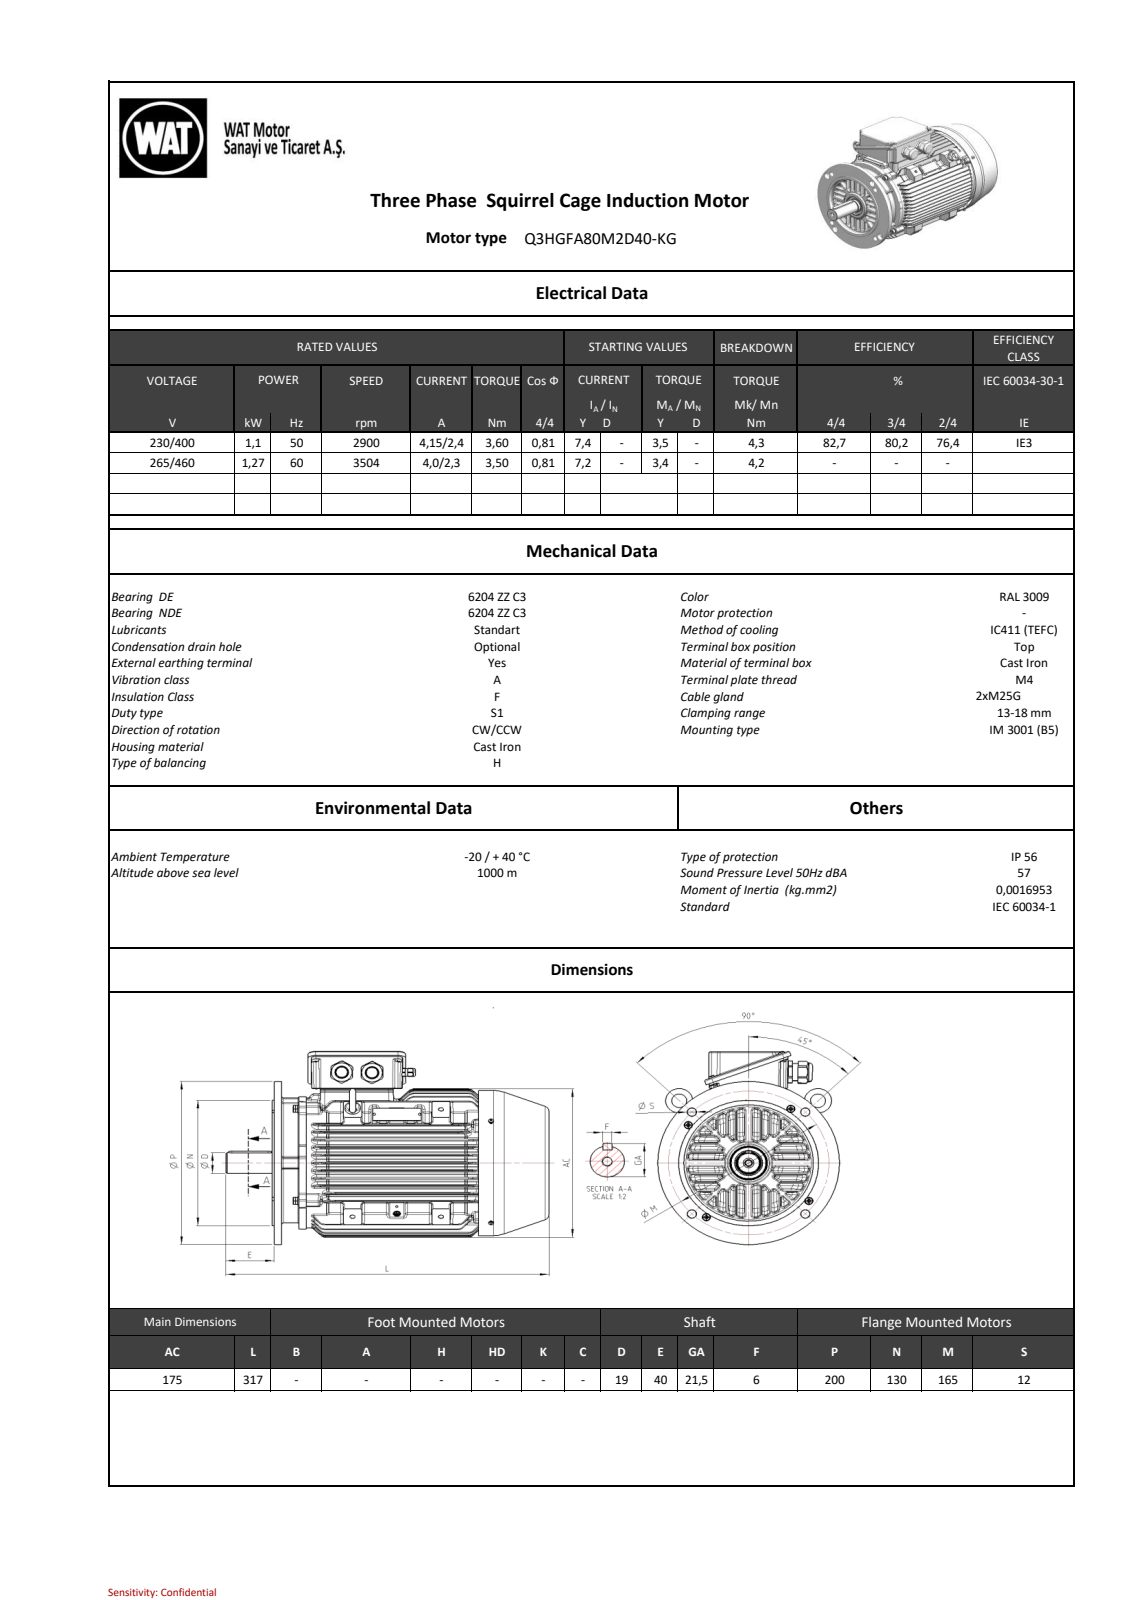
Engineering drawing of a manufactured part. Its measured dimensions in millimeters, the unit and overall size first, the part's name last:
Units: millimetres
Overall size (bounding box): 316.76 × 244.98 × 221.33
Round holes (diameter × count): ⌀10 ×6, ⌀12 ×4, ⌀2.5 ×2, ⌀17.2 ×2, ⌀5 ×1, ⌀6.4 ×1, ⌀6.5 ×1, ⌀27.8 ×1, ⌀168 ×1
Round bosses / shafts (diameter × count): ⌀20 ×4, ⌀8.65 ×3, ⌀8 ×3, ⌀5 ×3, ⌀27.7 ×2, ⌀25.25 ×2, ⌀200 ×1, ⌀170 ×1
Partial cylindrical surfaces — rounded edges, fillets, slot ends (radius × count): R1.5 ×355, R2.5 ×57, R2 ×54, R1 ×24, R4 ×18, R3 ×13, R7 ×13, R5 ×12
Main face-to-face distances: 5, 229.98, 234.98, 41.78, 271.76, 276.76, 62.56, 3, 3.01, 1.5
Hole centre spacings: 116.67, 133.37, 21.53, 61.25, 77, 82.5, 97.19, 126.58
Bodies: 0 solids, 2955 faces (801 planar, 845 cylindrical, 1309 other)
Part name (STEP PRODUCT): C90125944CFF0j5g
STEP written by: SIEMENS PLM Software NX 11.0 (AUTOMOTIVE_DESIGN)
